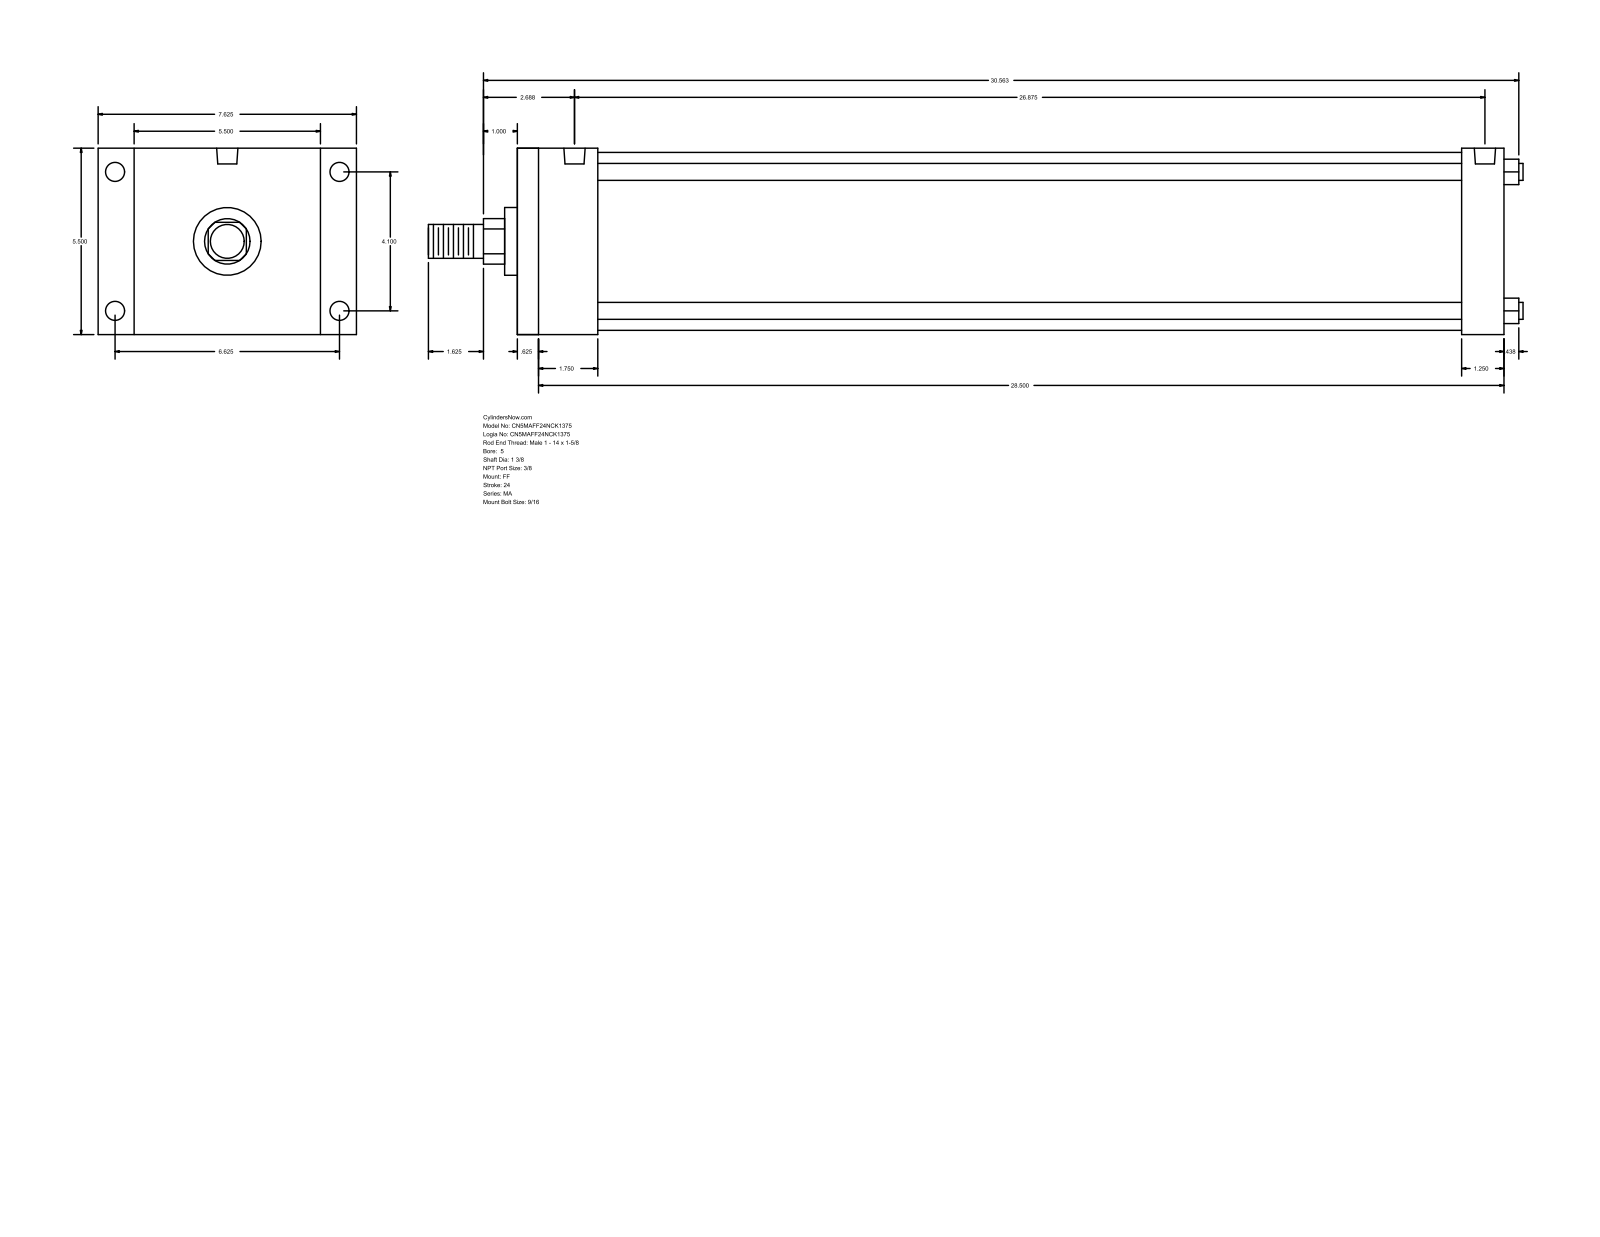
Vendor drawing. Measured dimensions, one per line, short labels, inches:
name: MA_FF__0500_1.375
written by: GSSL Pune (CONFIG_CONTROL_DESIGN)
unit: in
bodies: 0 solids, 92 faces (64 planar, 28 cylindrical, 0 other)
size: 32.313 × 7.625 × 5.5
holes: 4× ⌀0.437, 4× ⌀0.563, 2× ⌀0.627
bosses: 4× ⌀0.5, 1× ⌀5.25, 1× ⌀2, 1× ⌀1.375, 1× ⌀1
rounds: 1× R0.672
face distances: 5.5, 29.125, 0.625, 28.5, 27.875, 27.25, 1.25, 2.375, 1.75, 25.5
hole spacings: 0.188, 4.1, 6.625, 7.791, 26.5, 26.687, 26.875
